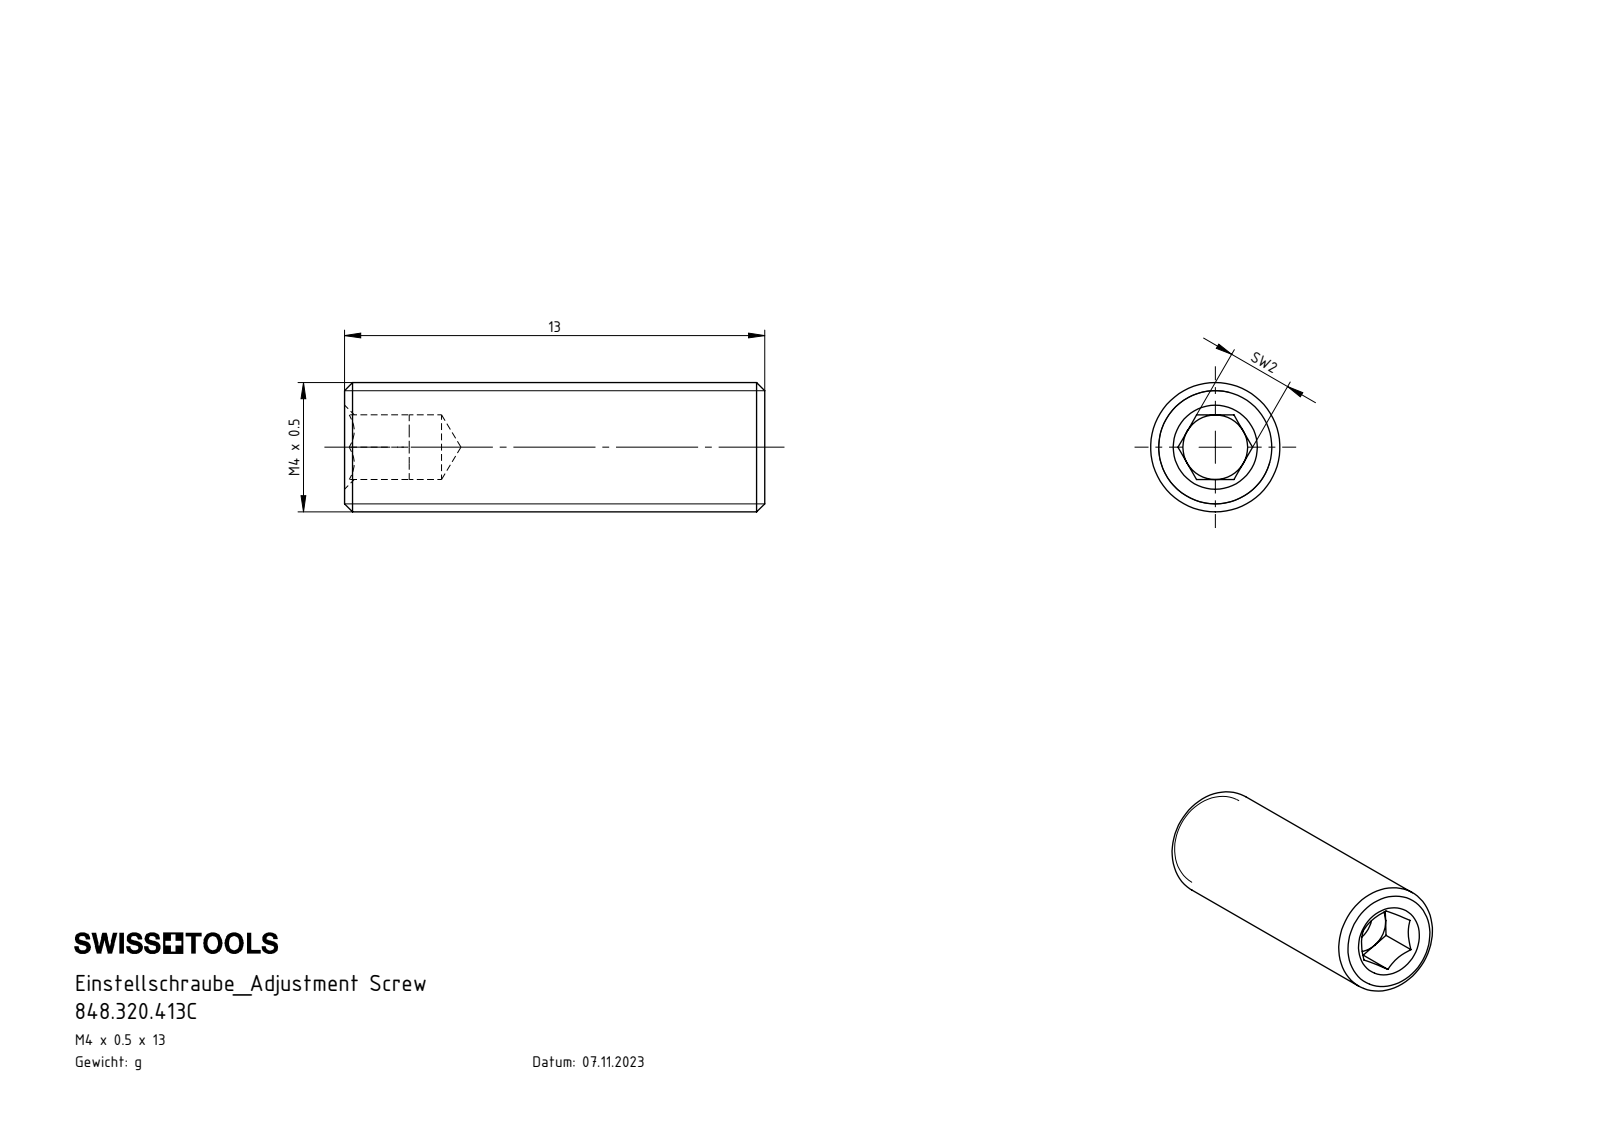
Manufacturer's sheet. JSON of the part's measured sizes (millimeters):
{"part_name": "848.320.413C", "step_written_by": "SolidWorks 2022 (AUTOMOTIVE_DESIGN)", "units": "millimeters", "bodies": {"solids": 1, "faces": 26, "planar": 14, "cylindrical": 4, "other": 8}, "overall_size": [13, 4, 4], "volume_mm3": 152, "surface_area_mm2": 204, "round_holes": [[2, 1]], "round_bosses_or_shafts": [[4, 1]], "face_to_face_distances": [2, 13, 11]}
